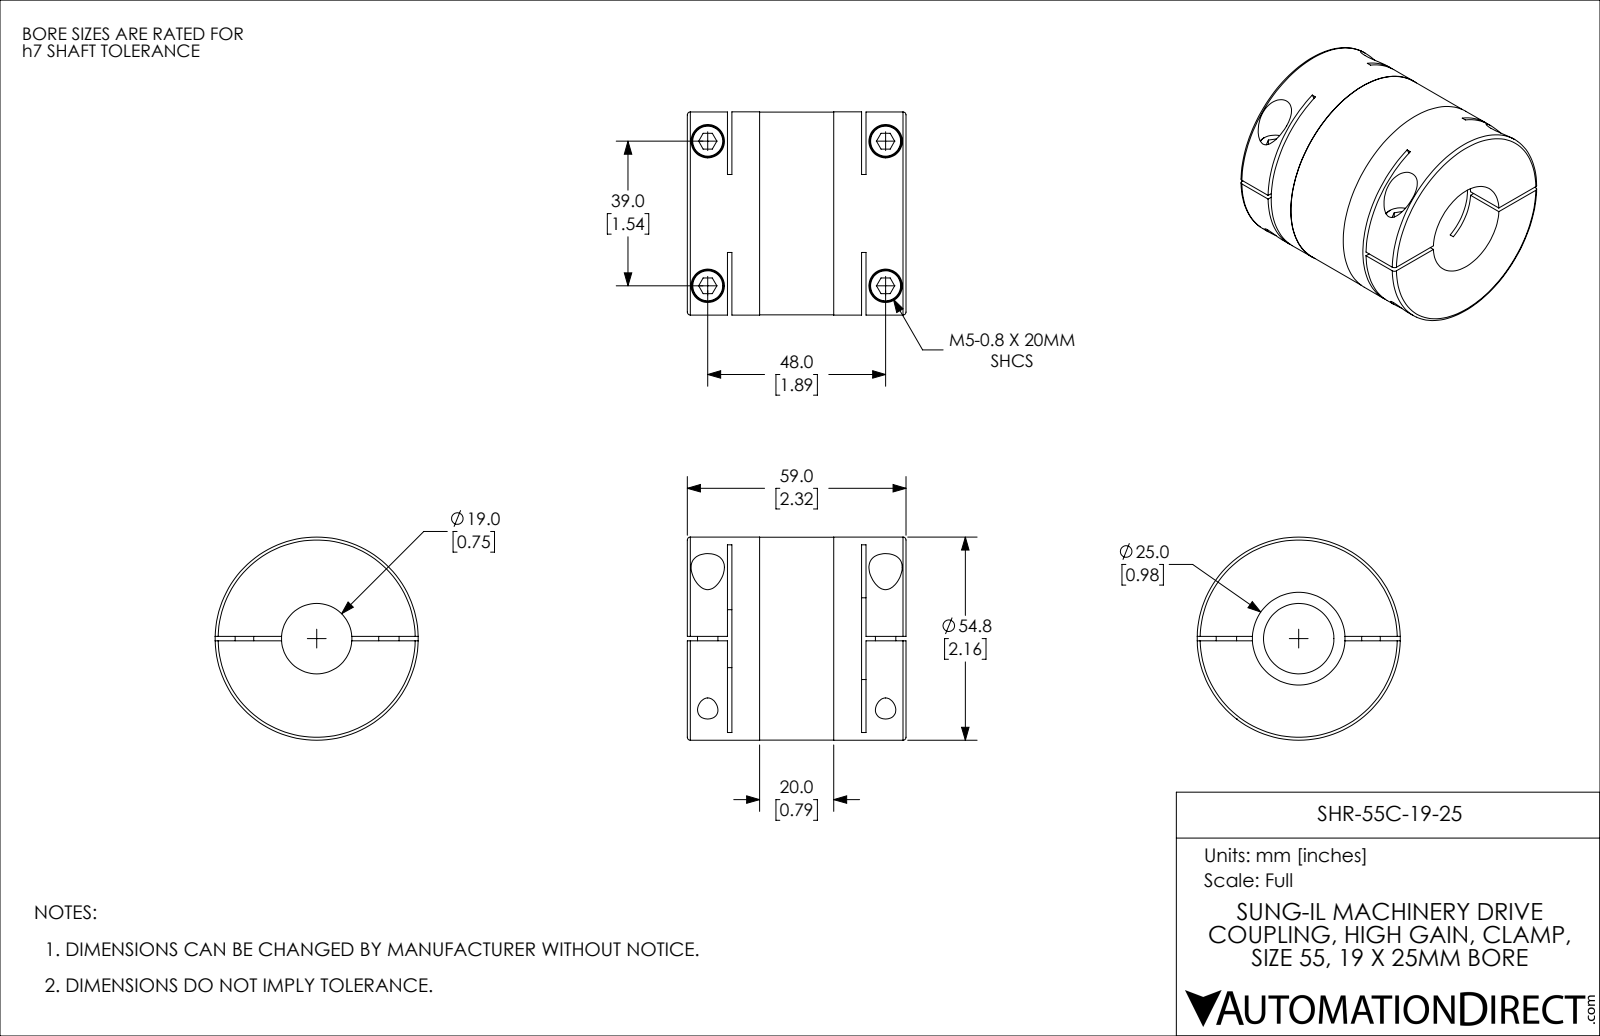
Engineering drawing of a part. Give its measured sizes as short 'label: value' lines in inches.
name: SHR-55C-19-25
written by: SolidWorks 2021 (CONFIG_CONTROL_DESIGN)
unit: in
bodies: 1 solid, 144 faces (70 planar, 58 cylindrical, 16 other)
size: 2.323 × 2.157 × 2.157
volume: 6.429 in³; area: 44.69 in²
holes: 4× ⌀0.217, 4× ⌀0.354, 1× ⌀0.748, 1× ⌀0.984, 1× ⌀1.063
bosses: 4× ⌀0.335, 2× ⌀0.197, 1× ⌀2.157, 1× ⌀2.154
rounds: 2× R2.362
face distances: 0.047, 0.472, 1.85, 0.425, 1.898, 1.425, 2.323, 1.378, 1.472, 0.768
hole spacings: 1.535, 1.89, 2.435
